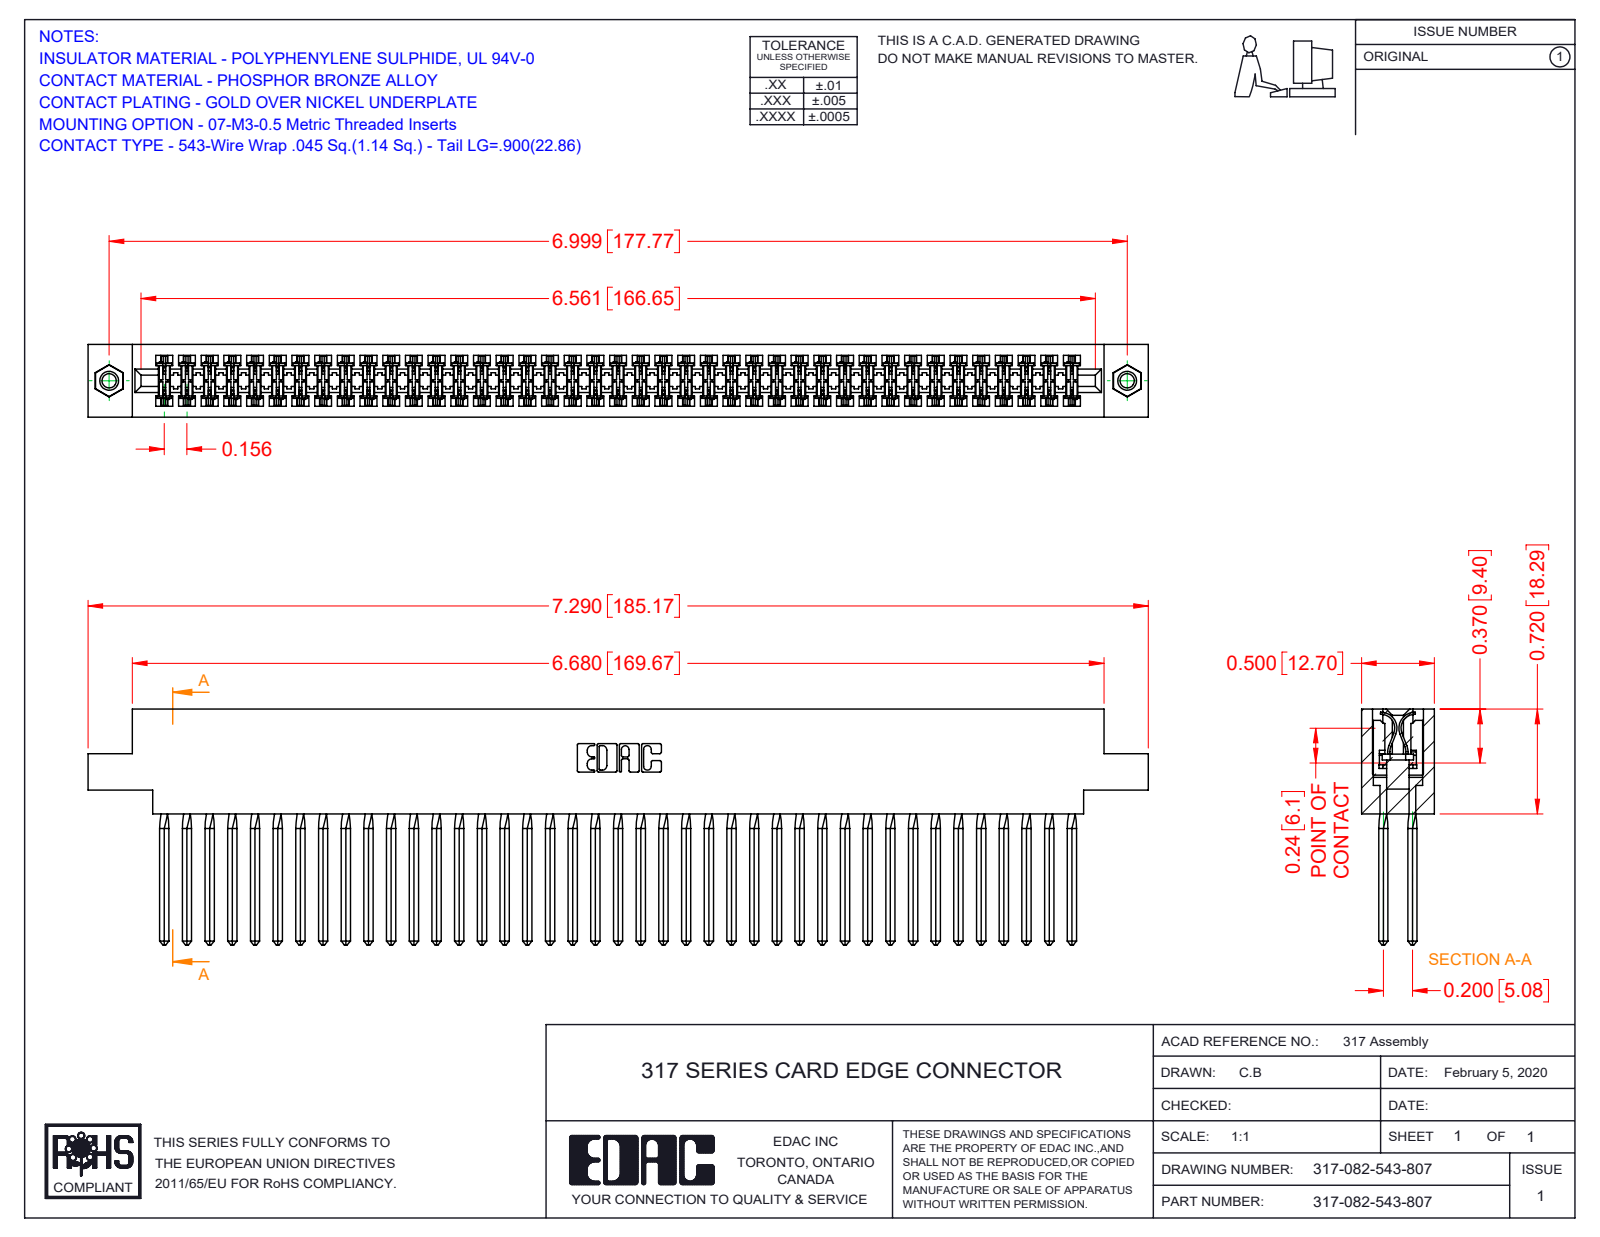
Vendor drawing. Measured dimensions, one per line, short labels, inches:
name: 317-082-543-807; 345-250-001_345-250-005-103; 317 Part_.156 Dia - TI; 317-290-001_543
written by: SolidWorks 2016 (CONFIG_CONTROL_DESIGN)
unit: in
bodies: 85 solids, 7460 faces (6076 planar, 1040 cylindrical, 344 other)
size: 7.29 × 1.62 × 0.5
volume: 1.918 in³; area: 73.92 in²
holes: 2× ⌀0.098, 2× ⌀0.125, 2× ⌀0.156
bosses: 2× ⌀0.155
rounds: 164× R0.015, 22× R0.01, 6× R0.007, 6× R0.031, 3× R0.026, 2× R0.095, 2× R0.1, 2× R0.11
face distances: 0.5, 0.075, 0.425, 0.35, 0.195, 0.11, 0.094, 0.2, 0.115, 0.131
hole spacings: 6.999
